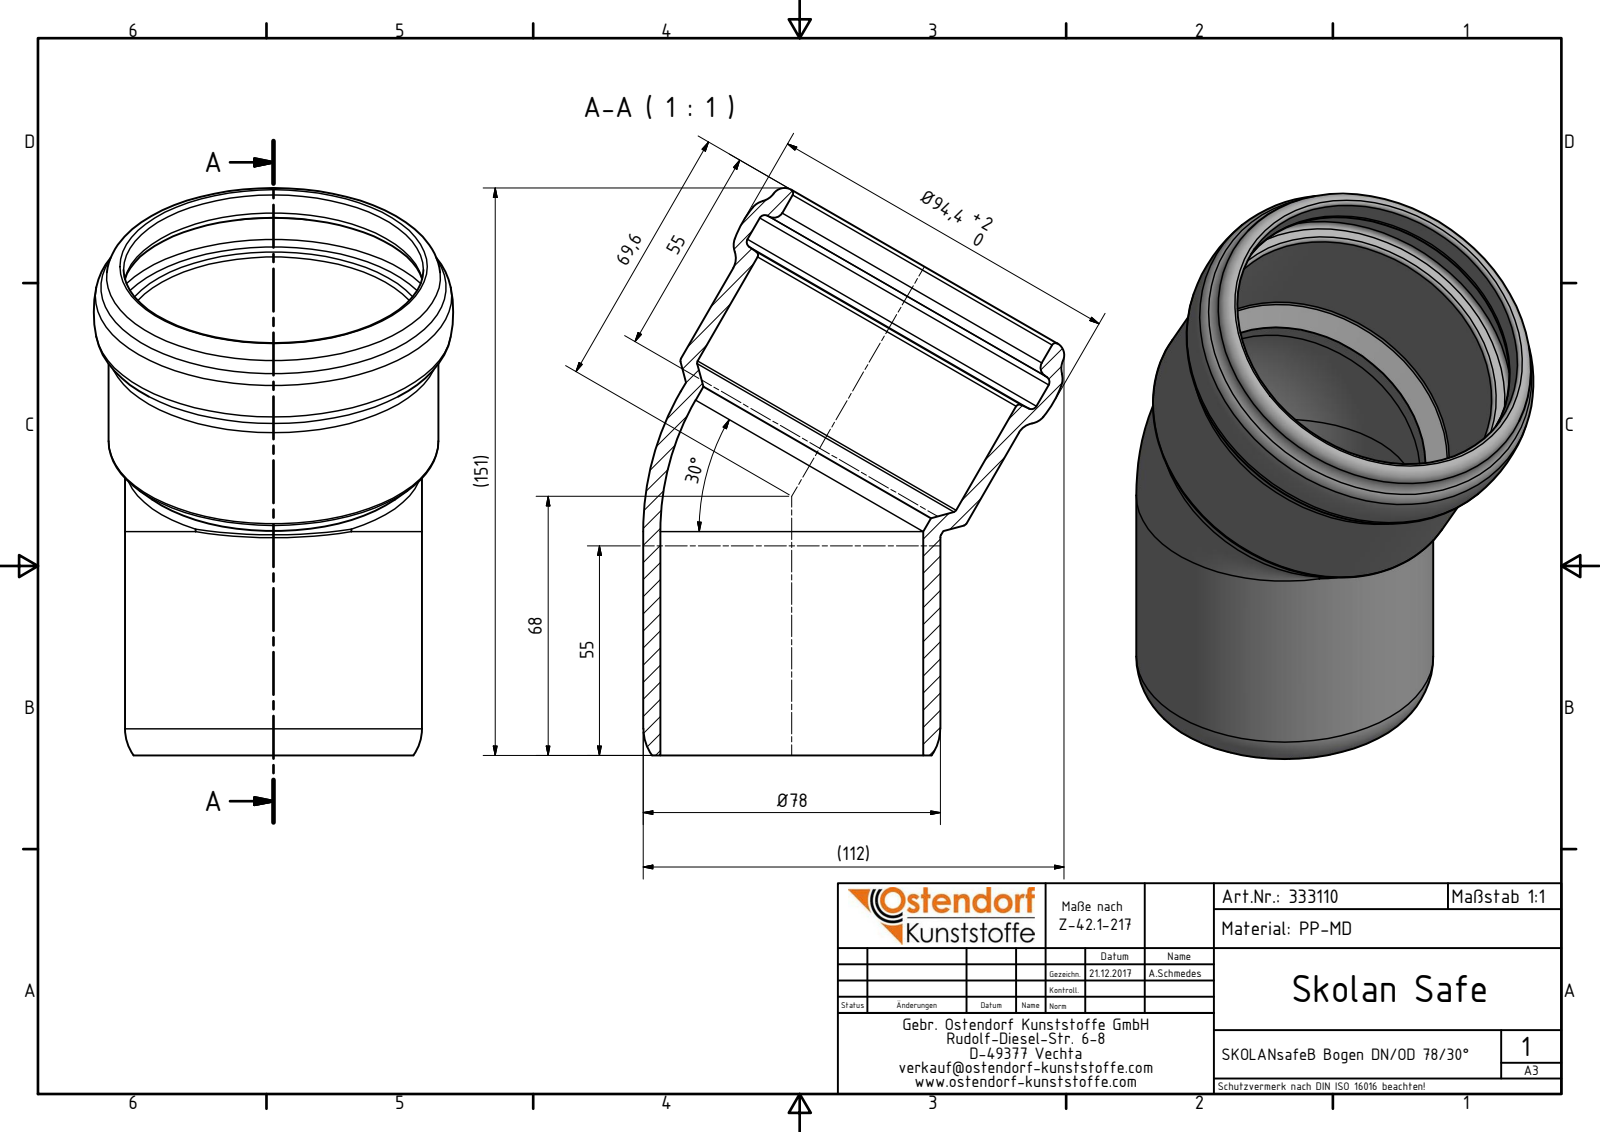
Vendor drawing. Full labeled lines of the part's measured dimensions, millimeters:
Part name (STEP PRODUCT): 333110 SKOLANsafeB Bogen DN_OD 78_30°
STEP written by: Autodesk Inventor 2016 (AUTOMOTIVE_DESIGN)
Units: millimetres
Bodies: 1 solid, 30 faces (1 planar, 8 cylindrical, 21 other)
Overall size (bounding box): 148.92 × 110.49 × 94.4
Volume: 148 249 mm³ · Surface area: 71 366 mm²
Round holes (diameter × count): ⌀69 ×2, ⌀78.4 ×1, ⌀78.7 ×1, ⌀87.6 ×1
Round bosses / shafts (diameter × count): ⌀78 ×2, ⌀86.6 ×1
